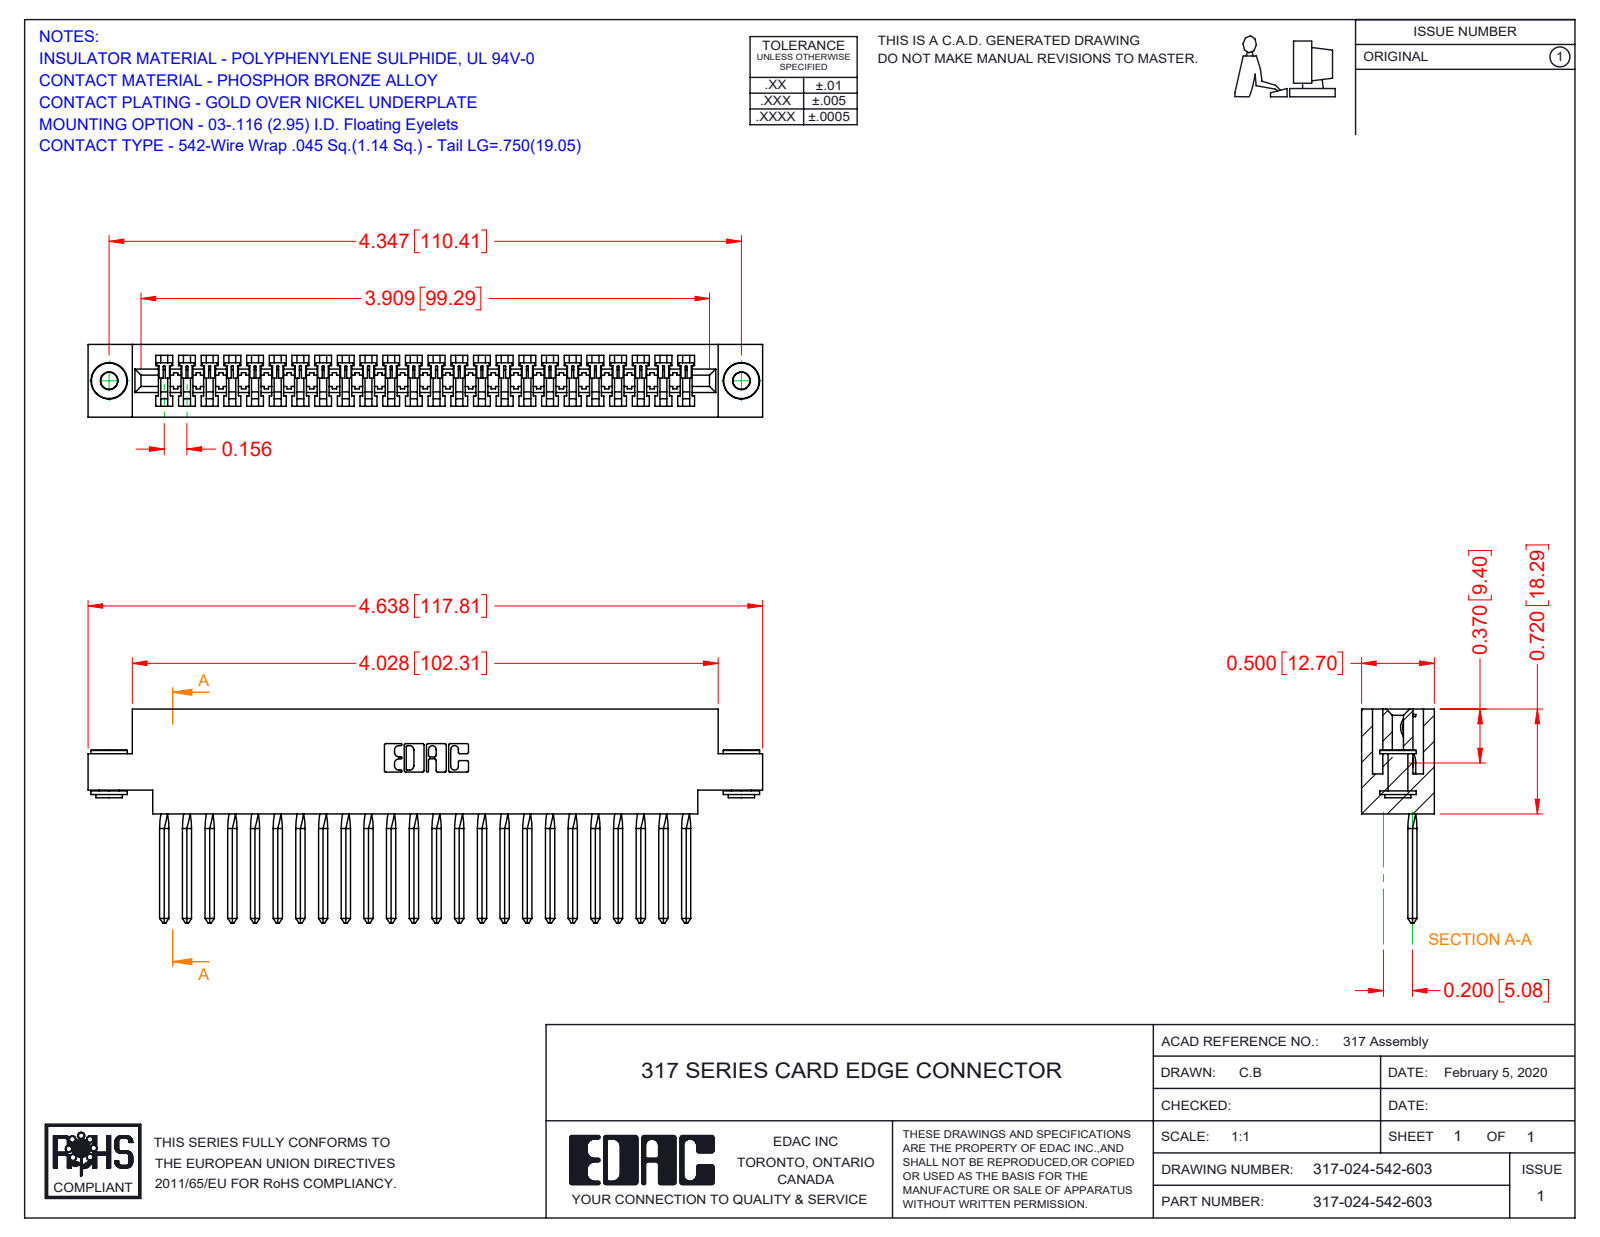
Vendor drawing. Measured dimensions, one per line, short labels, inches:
name: 317-024-542-603; 317-290-003_542; 345-250-002_345-250-002-102; 317 Part_.156 Dia - TH
written by: SolidWorks 2016 (CONFIG_CONTROL_DESIGN)
unit: in
bodies: 27 solids, 1940 faces (1604 planar, 232 cylindrical, 104 other)
size: 4.638 × 1.47 × 0.5
volume: 1.082 in³; area: 33.26 in²
holes: 2× ⌀0.116, 2× ⌀0.156
bosses: 2× ⌀0.25, 2× ⌀0.18, 2× ⌀0.136
rounds: 48× R0.006, 22× R0.01, 6× R0.007, 6× R0.031, 3× R0.026, 1× R0.074, 1× R0.089, 1× R0.1
face distances: 0.5, 0.075, 0.425, 0.35, 0.11, 0.136, 0.72, 0.279, 0.211, 0.289
hole spacings: 4.347
